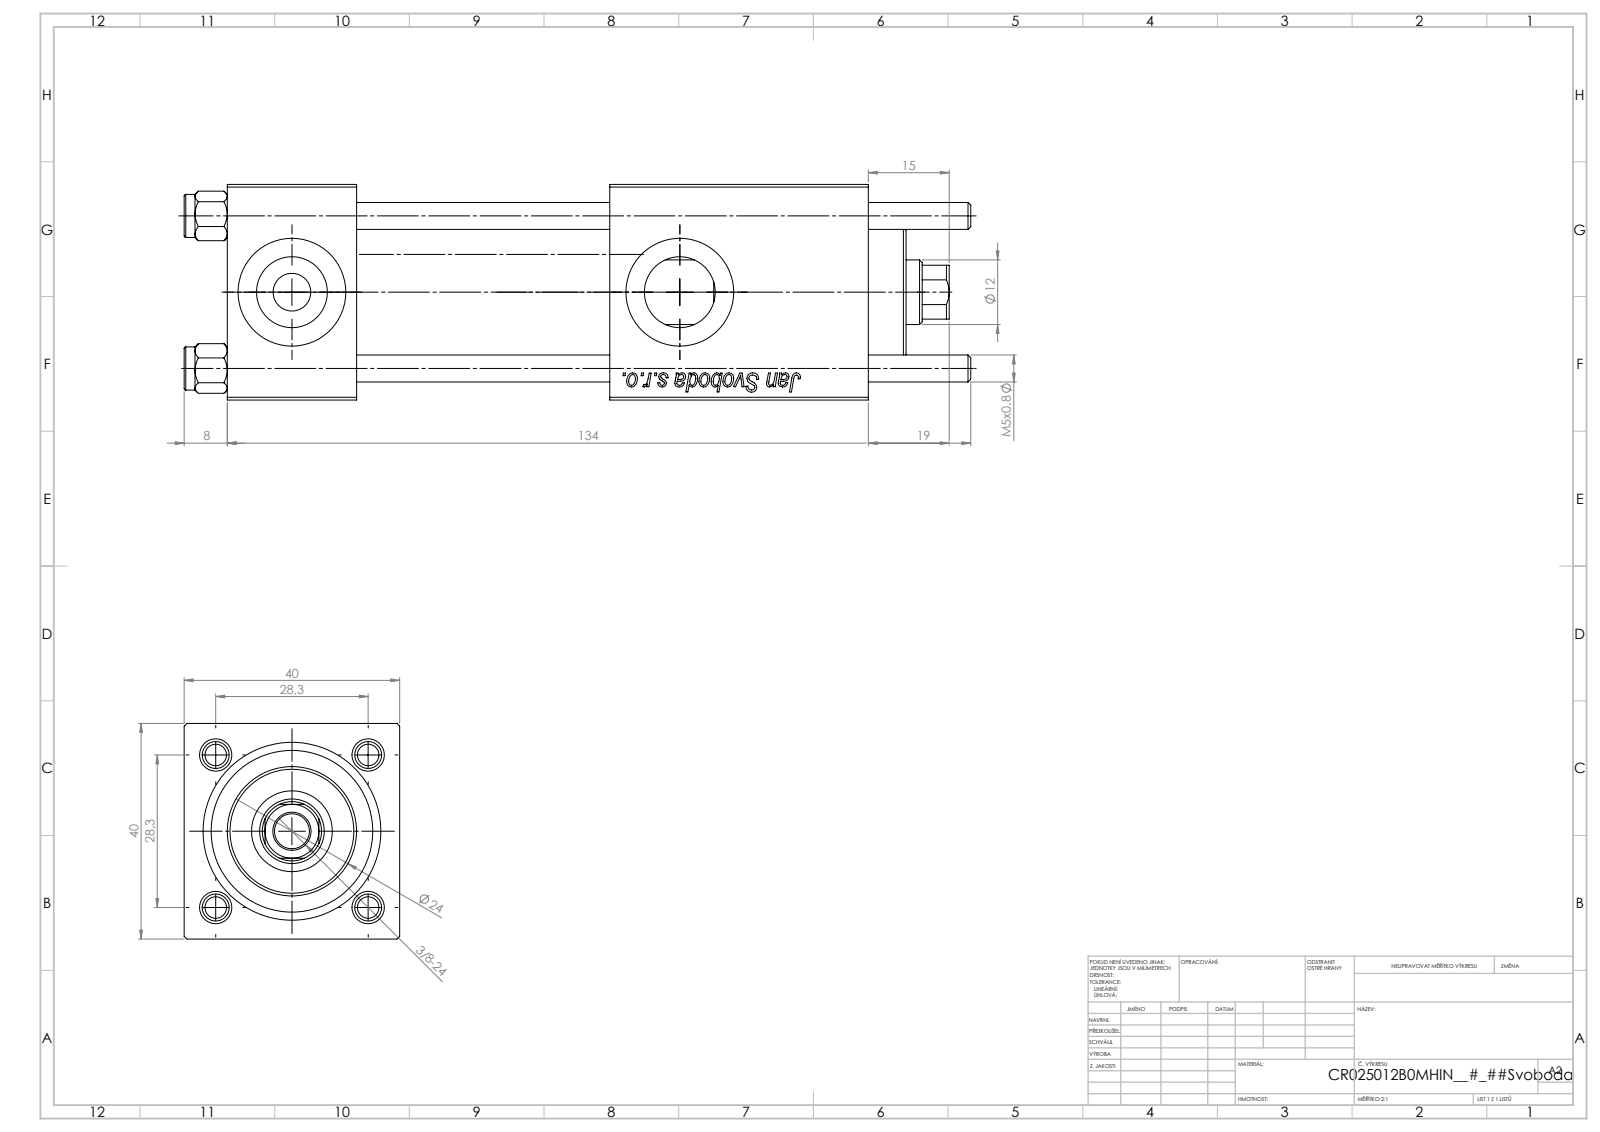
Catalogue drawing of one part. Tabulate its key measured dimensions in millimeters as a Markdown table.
| quantity | value |
| --- | --- |
| part name | V215CR_B-1; V215_VC_A; V215CR_VCP_B; NUT_M5_B (+1 more) |
| STEP written by | SolidWorks 2019 (CONFIG_CONTROL_DESIGN) |
| units | millimeters |
| bodies | 11 solids, 1155 faces (429 planar, 78 cylindrical, 648 other) |
| overall size | 146 × 40 × 40 |
| volume | 144 884 mm³ |
| surface area | 58 619 mm² |
| round holes (diameter × count) | 5 × 4, 20 × 3, 7 × 2, 13.16 × 2, 6.5 × 1, 12 × 1, 15 × 1, 25 × 1, 30 × 1 |
| round bosses / shafts (diameter × count) | 8 × 4, 31 × 1, 24 × 1 |
| partial cylindrical surfaces (radius × count) | 5.5 × 1 |
| main face-to-face distances | 40, 24, 90.3, 66.3, 71, 47, 19.3, 119, 95, 48 |
| hole center spacings | 20.01, 28.3, 40.02, 72 |
